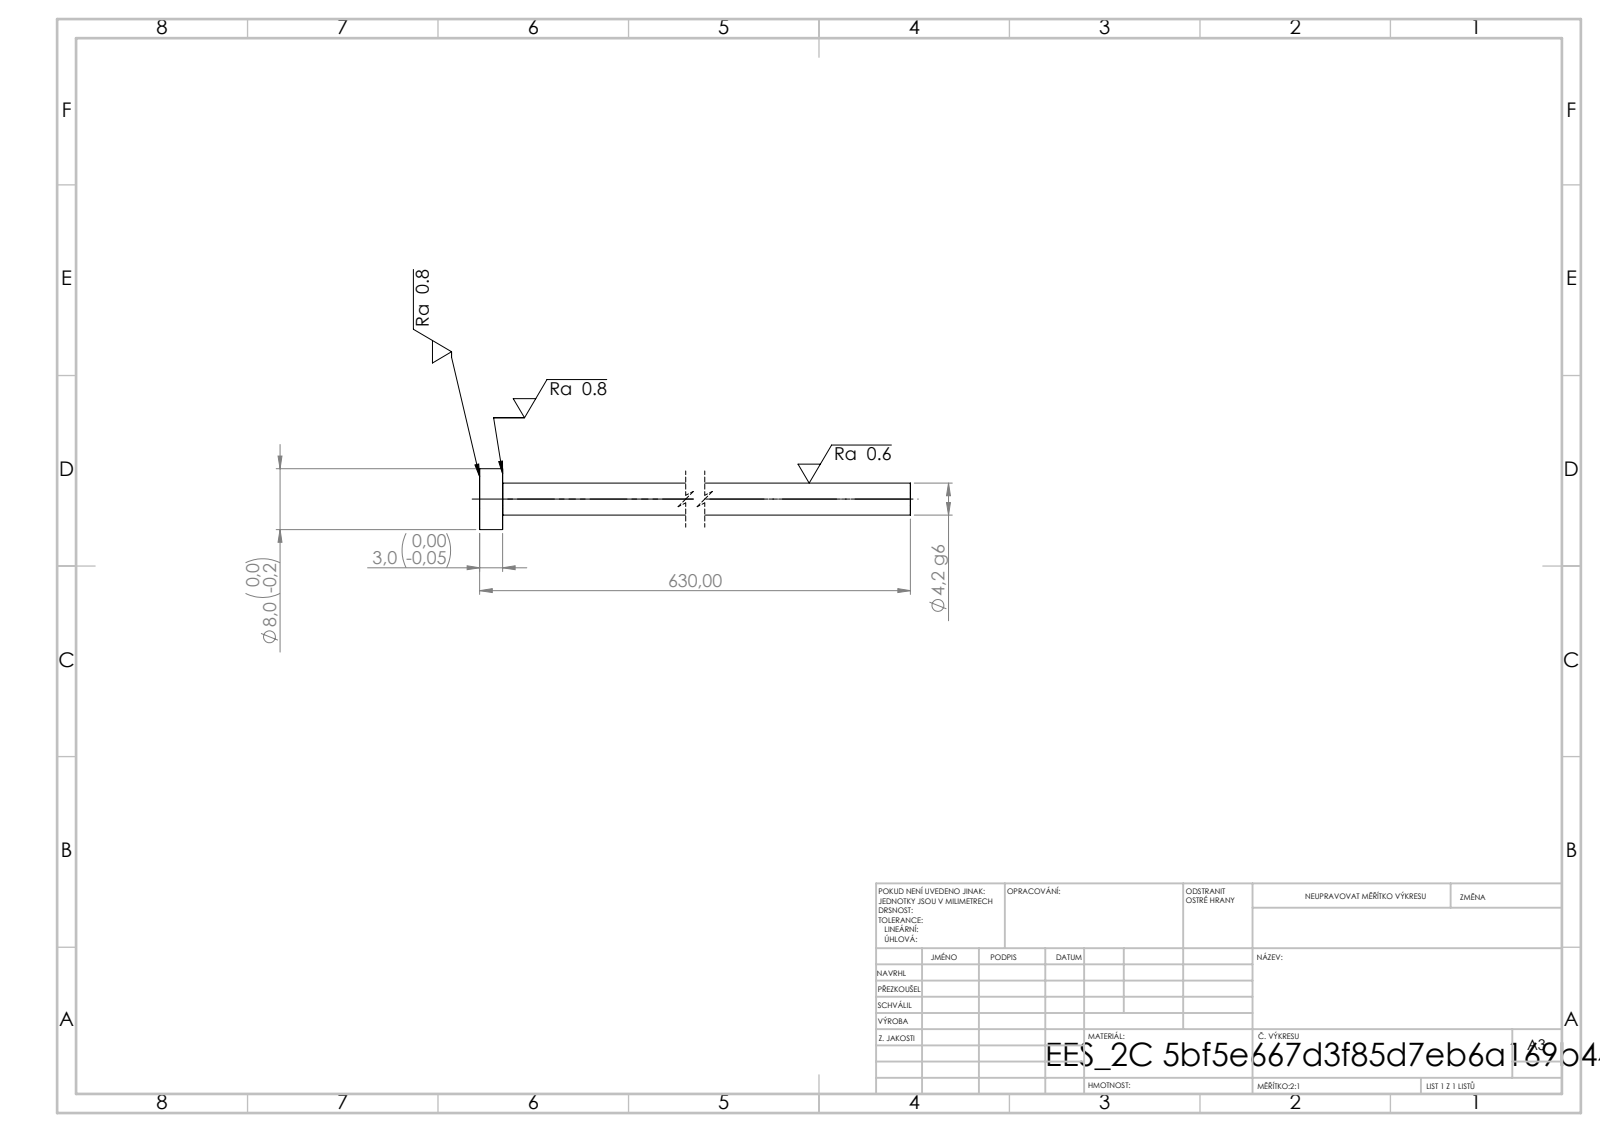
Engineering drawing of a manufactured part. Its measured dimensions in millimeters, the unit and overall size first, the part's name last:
Units: millimetres
Overall size (bounding box): 630 × 8 × 8
Round bosses / shafts (diameter × count): ⌀8 ×1, ⌀4.2 ×1
Main face-to-face distances: 3, 630, 627
Volume: 8 838 mm³ · Surface area: 8 449 mm²
Bodies: 1 solid, 7 faces (3 planar, 4 cylindrical, 0 other)
STEP written by: SolidWorks 2019 (CONFIG_CONTROL_DESIGN)
